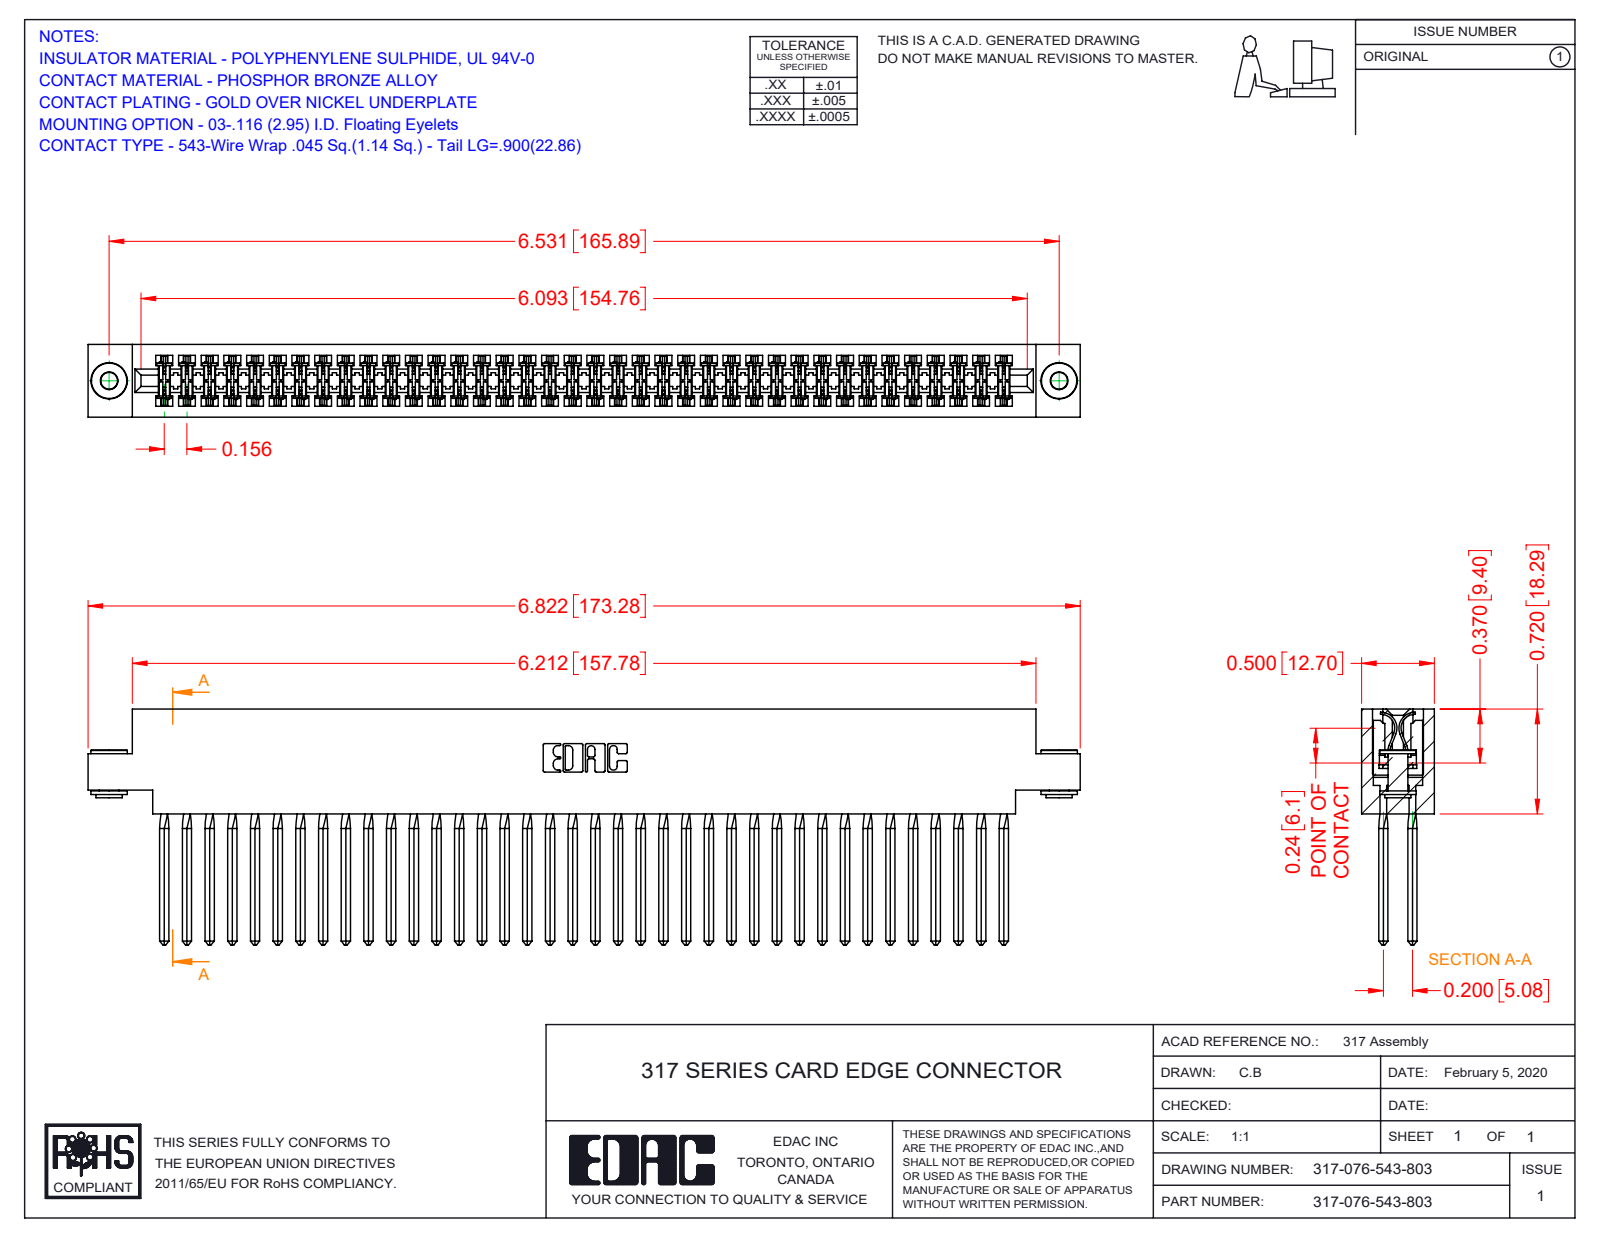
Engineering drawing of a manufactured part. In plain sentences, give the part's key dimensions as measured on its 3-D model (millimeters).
The part is named "345-250-002_345-250-002-102; 317-290-001_543; 317 Part_.156 Dia - TH; 317-076-543-803". Its 3-D file was written by "SolidWorks 2016 (CONFIG_CONTROL_DESIGN)". It is 79 solids with 6904 faces: 5616 planar, 976 cylindrical and 312 other. Overall it measures 173.3 by 41.1 by 12.7 millimeters. Its volume is 29 350 cubic millimeters and its surface area 44 570 square millimeters. Round holes: 2 of diameter 2.9, 2 of diameter 4. Round bosses or shafts: 2 of diameter 6.4, 2 of diameter 4.6, 2 of diameter 3.5. Partial cylindrical surfaces (rounded edges, fillets, slot ends): 152 of radius 0.4, 22 of radius 0.3, 6 of radius 0.2, 6 of radius 0.8, 3 of radius 0.7, 2 of radius 2.4, 2 of radius 2.5, 2 of radius 2.8. The main face-to-face distances are 12.7, 1.9, 10.8, 8.9, 2.8, 5, 2.4, 5.1, 2.9, 3.3. The hole center spacings are 165.9.
